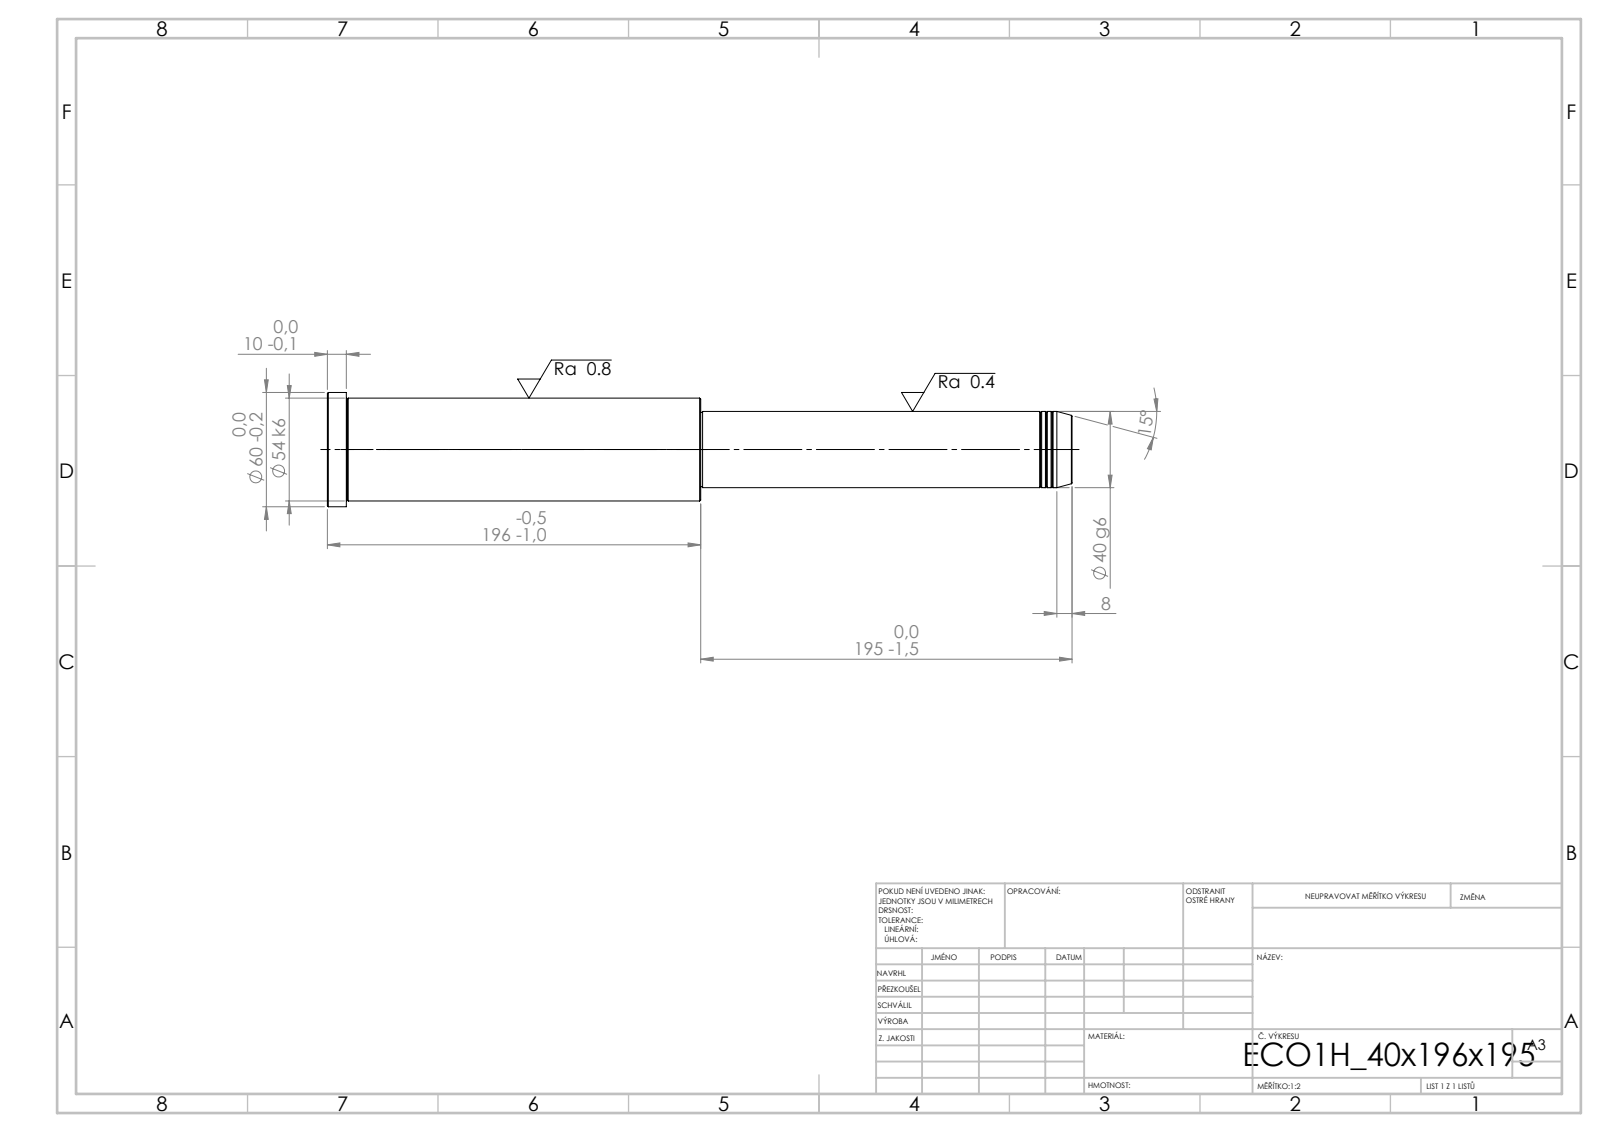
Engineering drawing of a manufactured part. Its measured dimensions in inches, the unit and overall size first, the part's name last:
Units: inches
Overall size (bounding box): 15.394 × 2.362 × 2.362
Round bosses / shafts (diameter × count): ⌀2.362 ×1, ⌀2.126 ×1, ⌀1.575 ×1, ⌀1.535 ×1
Main face-to-face distances: 7.717, 7.677, 15.394, 15, 7.323, 0.394, 7.638, 0.039, 7.362, 7.756
Volume: 42.59 in³ · Surface area: 98.62 in²
Bodies: 1 solid, 43 faces (5 planar, 14 cylindrical, 24 other)
STEP written by: SolidWorks 2019 (CONFIG_CONTROL_DESIGN)
